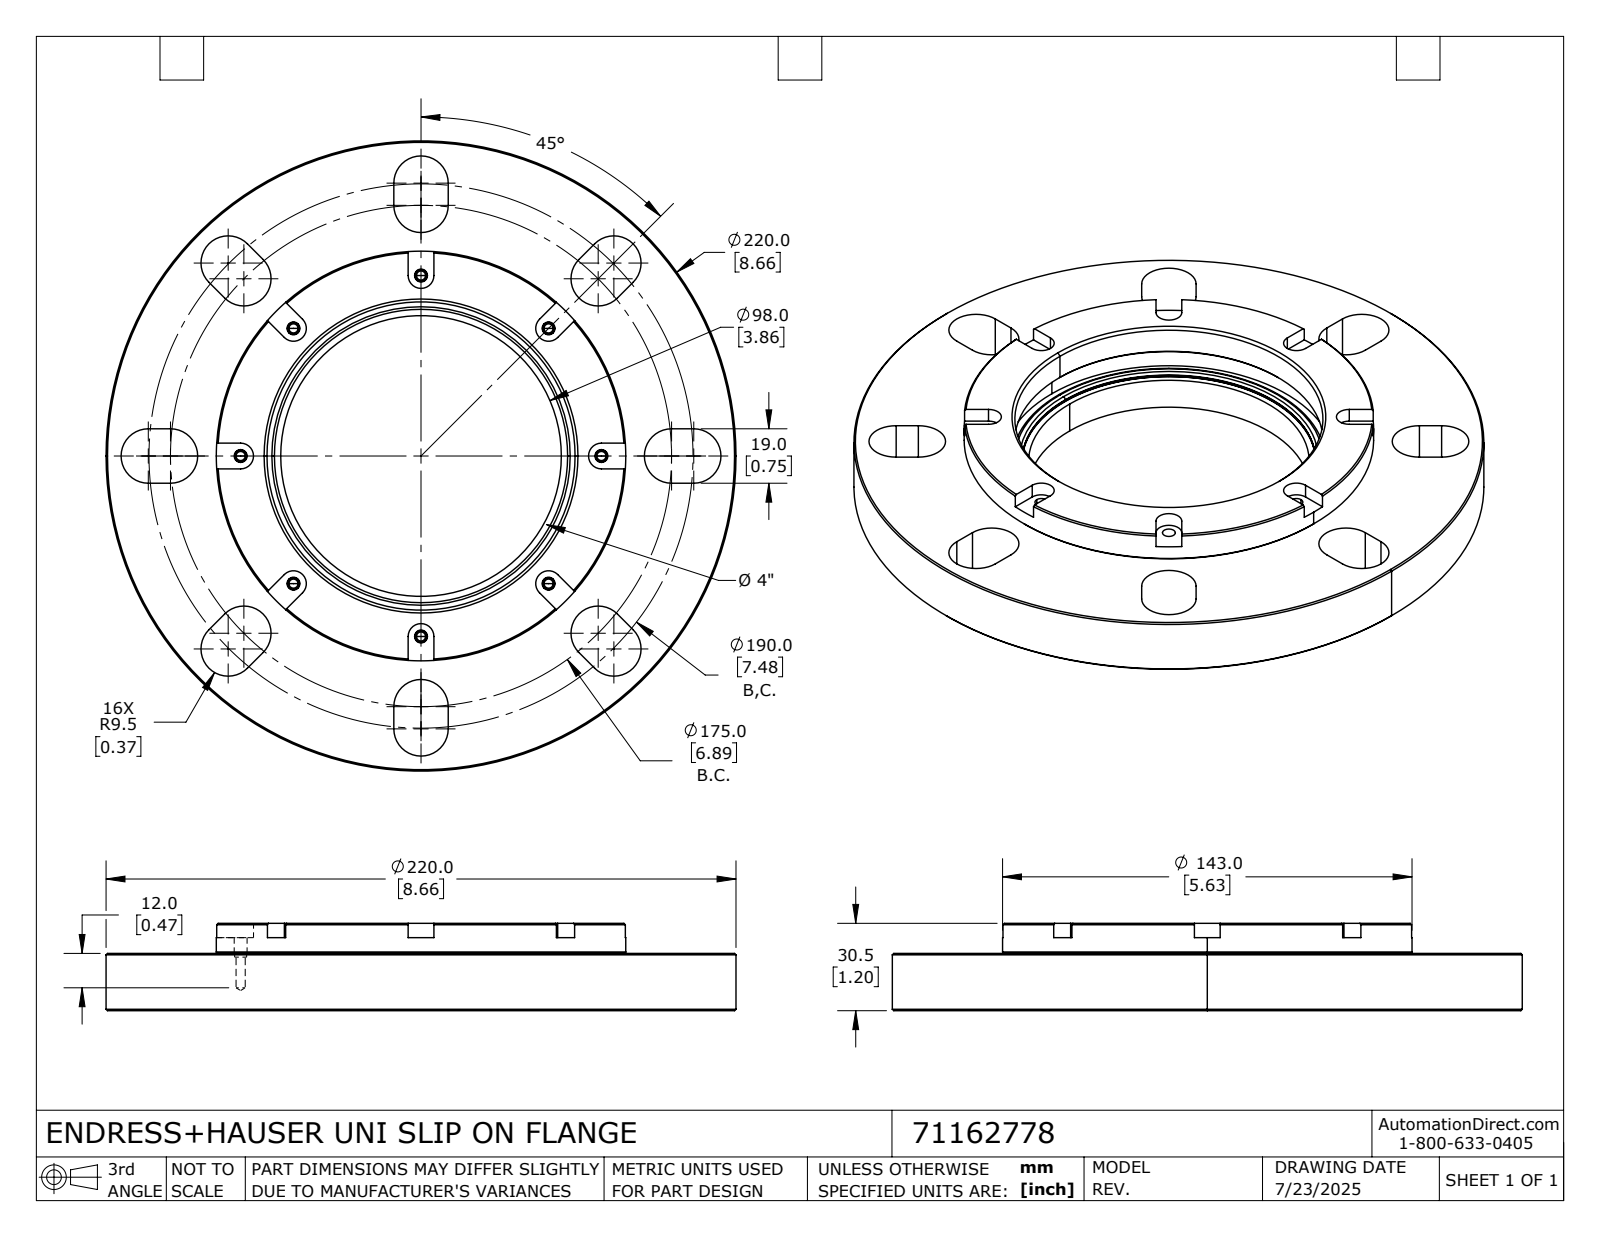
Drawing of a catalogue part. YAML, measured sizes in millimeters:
part_name: "71162778"
step_written_by: "SolidWorks 2024 (AUTOMOTIVE_DESIGN)"
units: millimeters
bodies: {solids: 3, faces: 238, planar: 57, cylindrical: 129, other: 52}
overall_size: [228.6, 228.6, 30.5]
volume: 642548
surface_area: 120993
round_holes:
  - {diameter: 3.2, count: 8}
  - {diameter: 4.2, count: 8}
  - {diameter: 4.5, count: 8}
  - {diameter: 98, count: 1}
  - {diameter: 102.4, count: 1}
  - {diameter: 107.6, count: 1}
  - {diameter: 109.2, count: 1}
  - {diameter: 115.6, count: 1}
round_bosses_or_shafts:
  - {diameter: 228.6, count: 1}
  - {diameter: 143, count: 1}
partial_cylinders:
  - {radius: 9.5, count: 16}
  - {radius: 4.5, count: 8}
face_to_face_distances: [20, 30.5, 10.5, 19, 11.5, 8.5, 1.97, 14, 5, 9.53]
hole_center_spacings: [48.22, 63, 89.1, 116.41, 126, 126.01]
